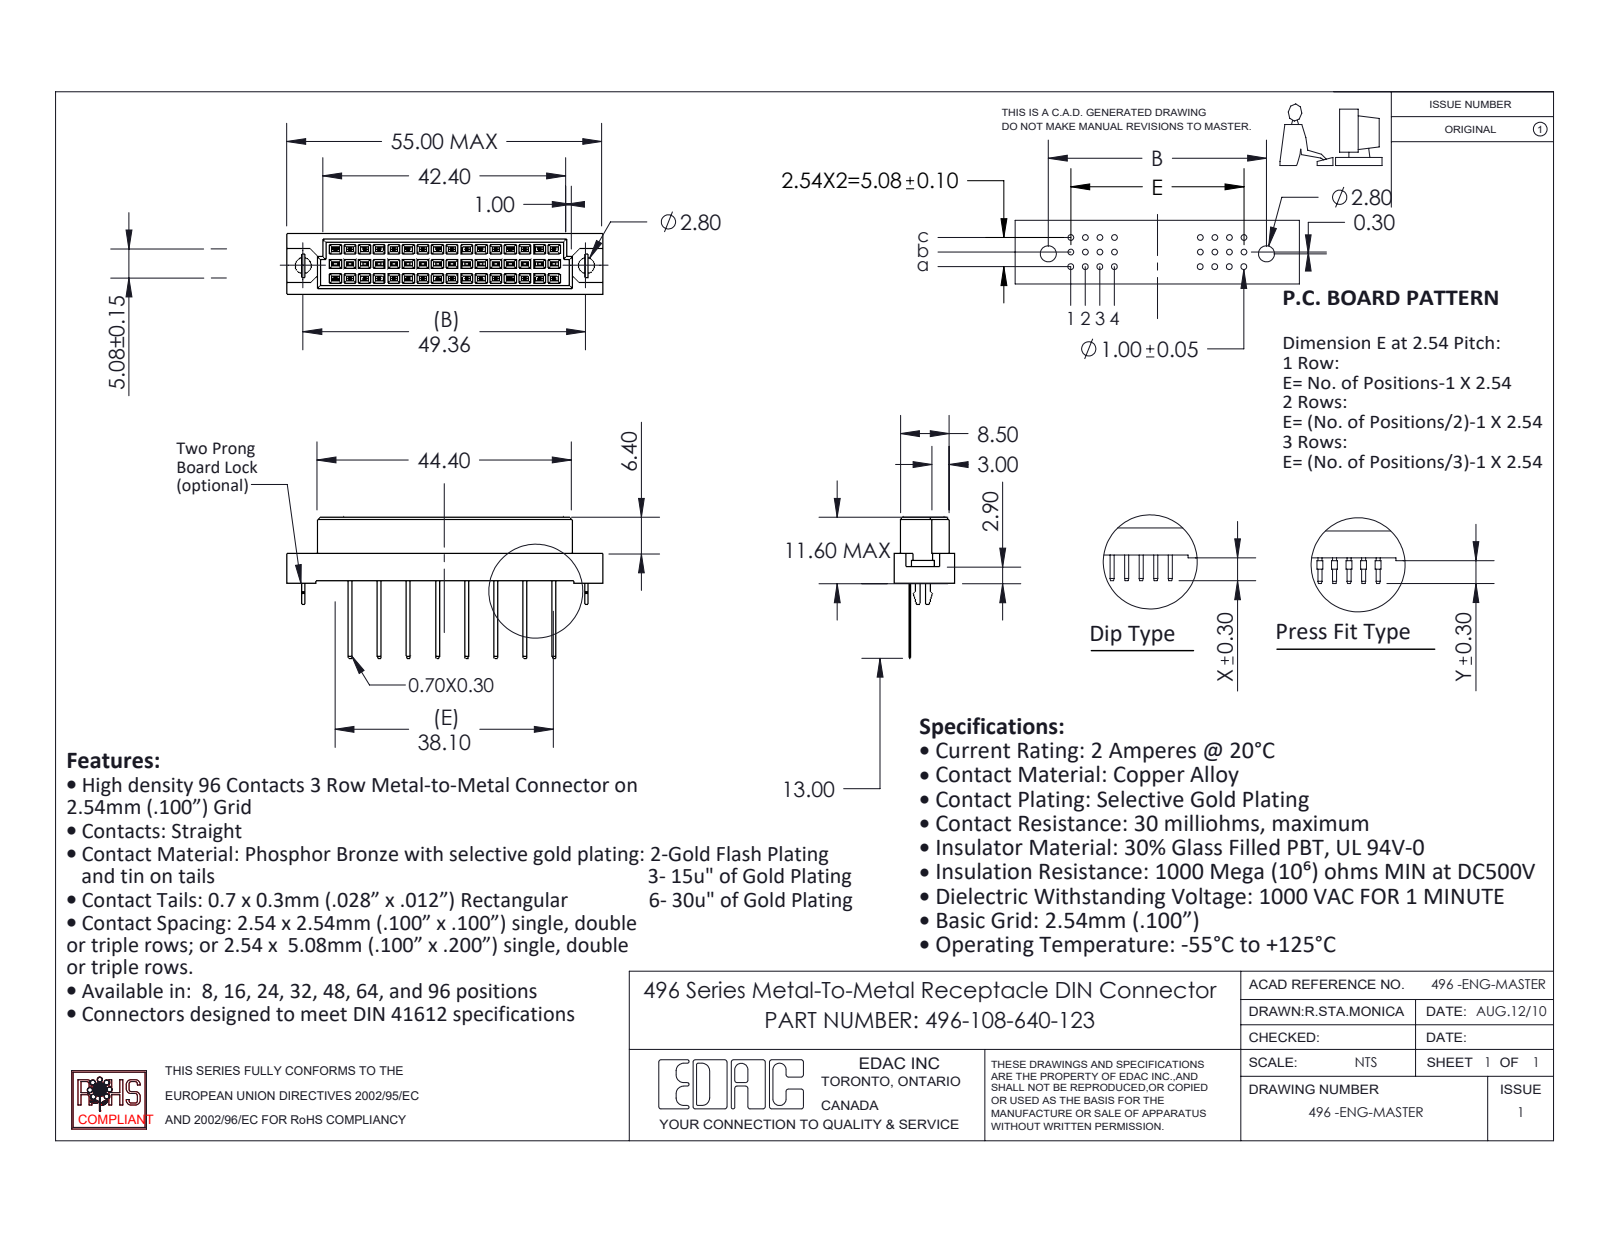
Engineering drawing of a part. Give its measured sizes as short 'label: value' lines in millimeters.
name: 496 Part_48; 496-290_40; 496-108-640-123; 496 Bore-lock
written by: SolidWorks 2020 (CONFIG_CONTROL_DESIGN)
unit: mm
bodies: 11 solids, 782 faces (776 planar, 6 cylindrical, 0 other)
size: 55 × 24.6 × 10.6
volume: 4 642 mm³; area: 4 615 mm²
holes: 2× ⌀2.8
rounds: 1× R0.53
face distances: 2.54, 1.05, 9.55, 5.08, 0.81, 10.6, 3.35, 1.73, 8.5, 0.56
hole spacings: 49.36
